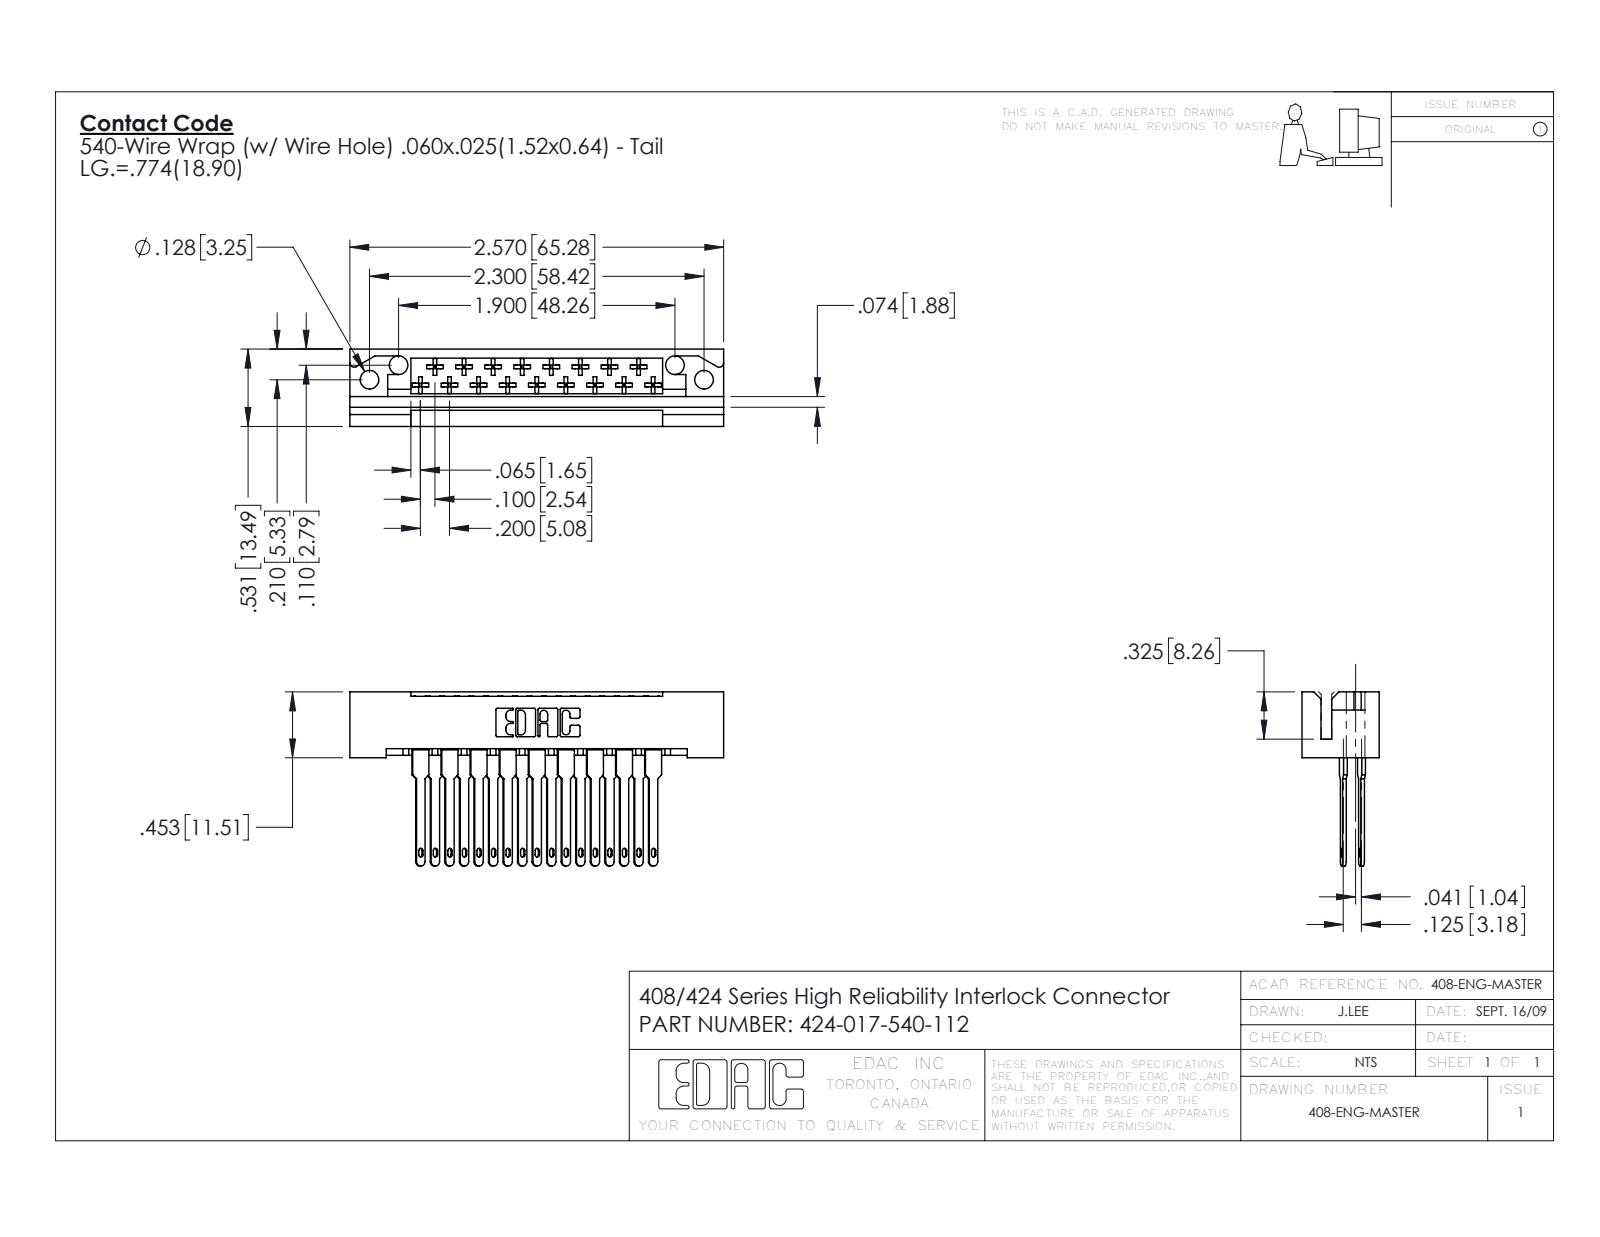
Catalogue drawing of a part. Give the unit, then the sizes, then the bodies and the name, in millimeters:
Units: millimetres
Overall size (bounding box): 65.3 × 30.4 × 13.5
Round holes (diameter × count): ⌀3.3 ×4
Partial cylindrical surfaces — rounded edges, fillets, slot ends (radius × count): R0.3 ×102, R0.4 ×34, R0.3 ×22, R0.5 ×19, R0.8 ×19, R0.2 ×6, R0.8 ×6, R0.7 ×3
Main face-to-face distances: 10.2, 0.6, 13.5, 3.2, 2.5, 3.3, 8.3, 1.9, 5.2, 0.6
Hole centre spacings: 5.7, 53.4, 48.3, 58.4
Volume: 7 370 mm³ · Surface area: 9 652 mm²
Bodies: 18 solids, 1114 faces (803 planar, 243 cylindrical, 68 other)
Part name (STEP PRODUCT): 424-017-540-112; 424 Part_017; 408-290-001_408-290-140
STEP written by: SolidWorks 2016 (CONFIG_CONTROL_DESIGN)
